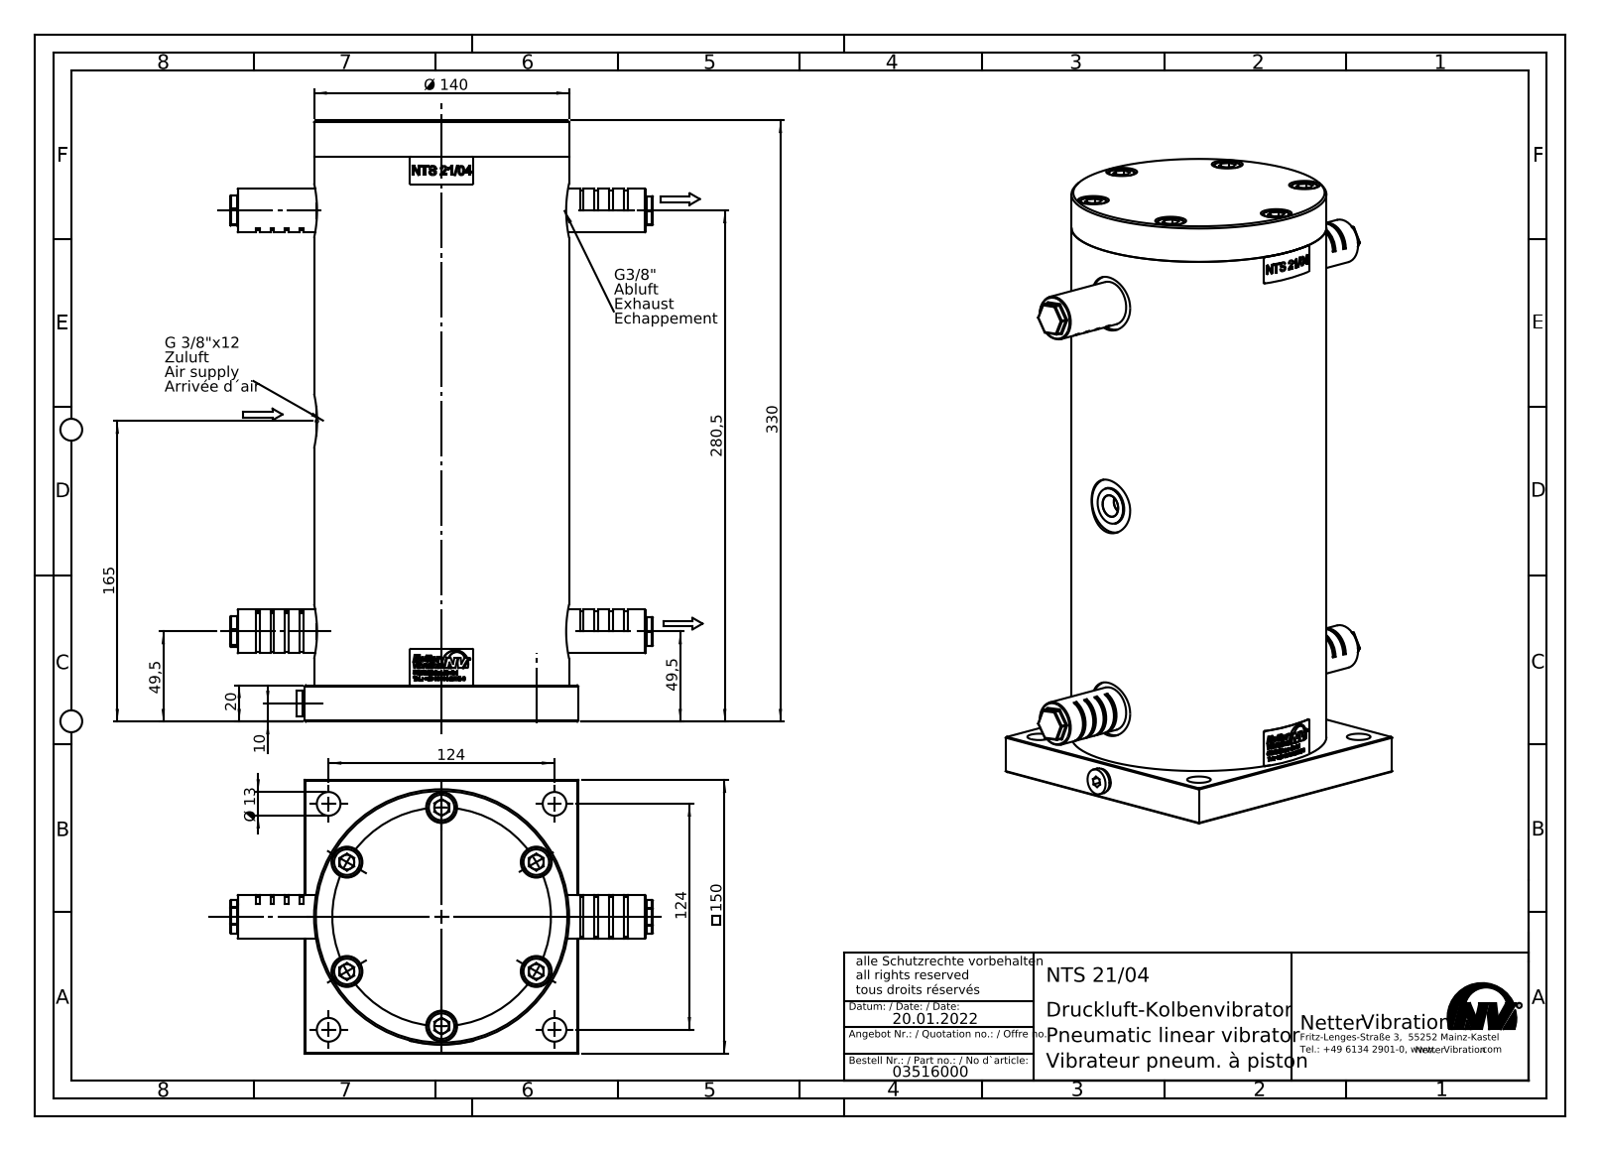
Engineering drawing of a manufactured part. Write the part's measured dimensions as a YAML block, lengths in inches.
part_name: "NTS 21-04 Kolbenvibrator #03516000"
step_written_by: "SolidWorks 2015 (AUTOMOTIVE_DESIGN)"
units: inches
bodies: {solids: 23, faces: 973, planar: 342, cylindrical: 399, other: 232}
overall_size: [12.992, 9.134, 5.906]
volume: 321.7
surface_area: 509.7
round_holes:
  - {diameter: 0.335, count: 6}
  - {diameter: 0.413, count: 6}
  - {diameter: 0.669, count: 6}
  - {diameter: 0.512, count: 4}
  - {diameter: 0.589, count: 3}
  - {diameter: 1.181, count: 3}
  - {diameter: 0.079, count: 1}
  - {diameter: 0.236, count: 1}
  - {diameter: 0.276, count: 1}
  - {diameter: 0.337, count: 1}
  - {diameter: 0.394, count: 1}
round_bosses_or_shafts:
  - {diameter: 0.63, count: 6}
  - {diameter: 0.394, count: 6}
  - {diameter: 0.945, count: 2}
  - {diameter: 0.656, count: 2}
  - {diameter: 5.512, count: 1}
  - {diameter: 0.866, count: 1}
  - {diameter: 0.551, count: 1}
  - {diameter: 0.512, count: 1}
partial_cylinders:
  - {radius: 0.02, count: 80}
  - {radius: 0.433, count: 1}
  - {radius: 2.764, count: 1}
face_to_face_distances: [0.787, 12.205, 11.417, 12.992, 5.906, 5.63, 0.276, 0.374, 0.413, 12.579]
hole_center_spacings: [2.362, 4.091, 1.32, 2.442, 3.452, 3.644, 4.66, 4.882]
